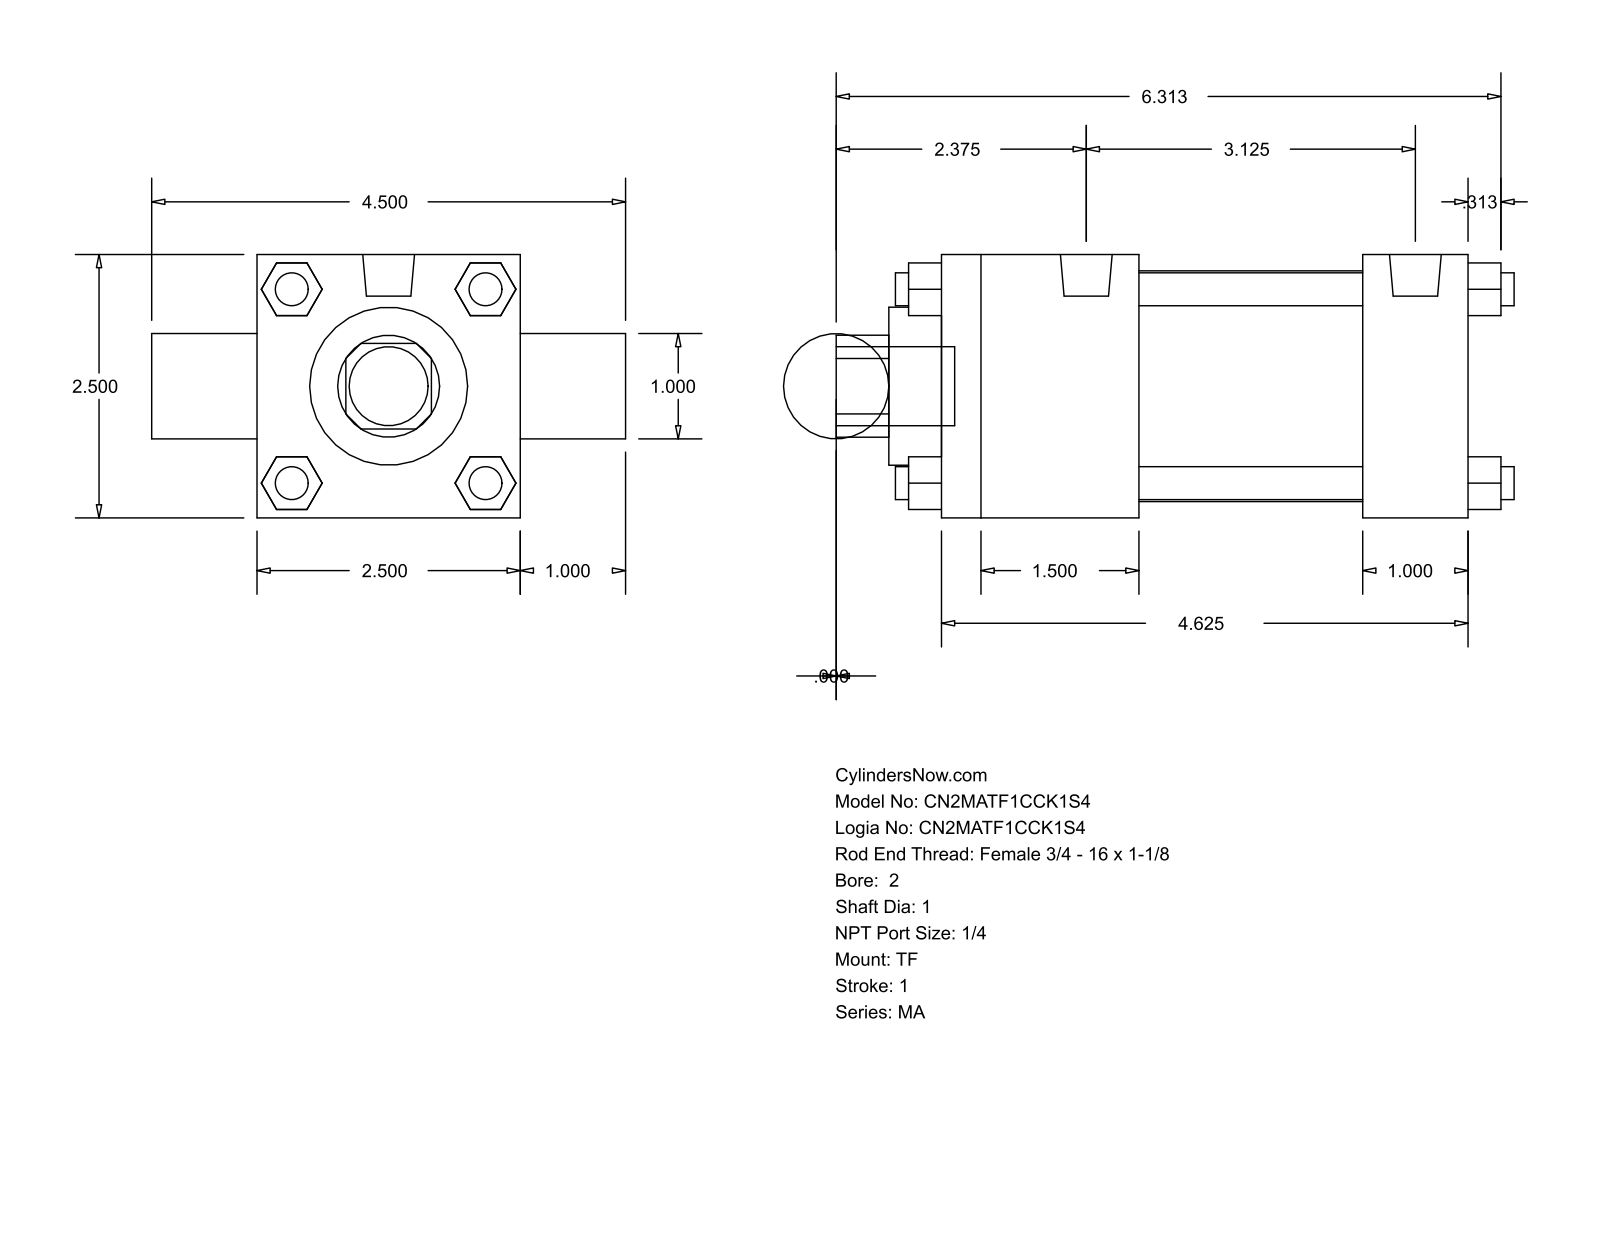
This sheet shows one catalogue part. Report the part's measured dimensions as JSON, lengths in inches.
{"part_name": "MA_TF__0200_1", "step_written_by": "GSSL Pune (CONFIG_CONTROL_DESIGN)", "units": "inches", "bodies": {"solids": 0, "faces": 120, "planar": 92, "cylindrical": 28, "other": 0}, "overall_size": [6.437, 4.5, 2.5], "round_holes": [[1, 2], [1.5, 1], [2.19, 1]], "round_bosses_or_shafts": [[0.313, 7], [0.492, 2], [0.75, 1]], "partial_cylinders_radius": [[0.484, 1]], "face_to_face_distances": [2.5, 1, 5, 0.5, 1.875, 4, 2.125, 3.125, 4.5, 3.5]}
